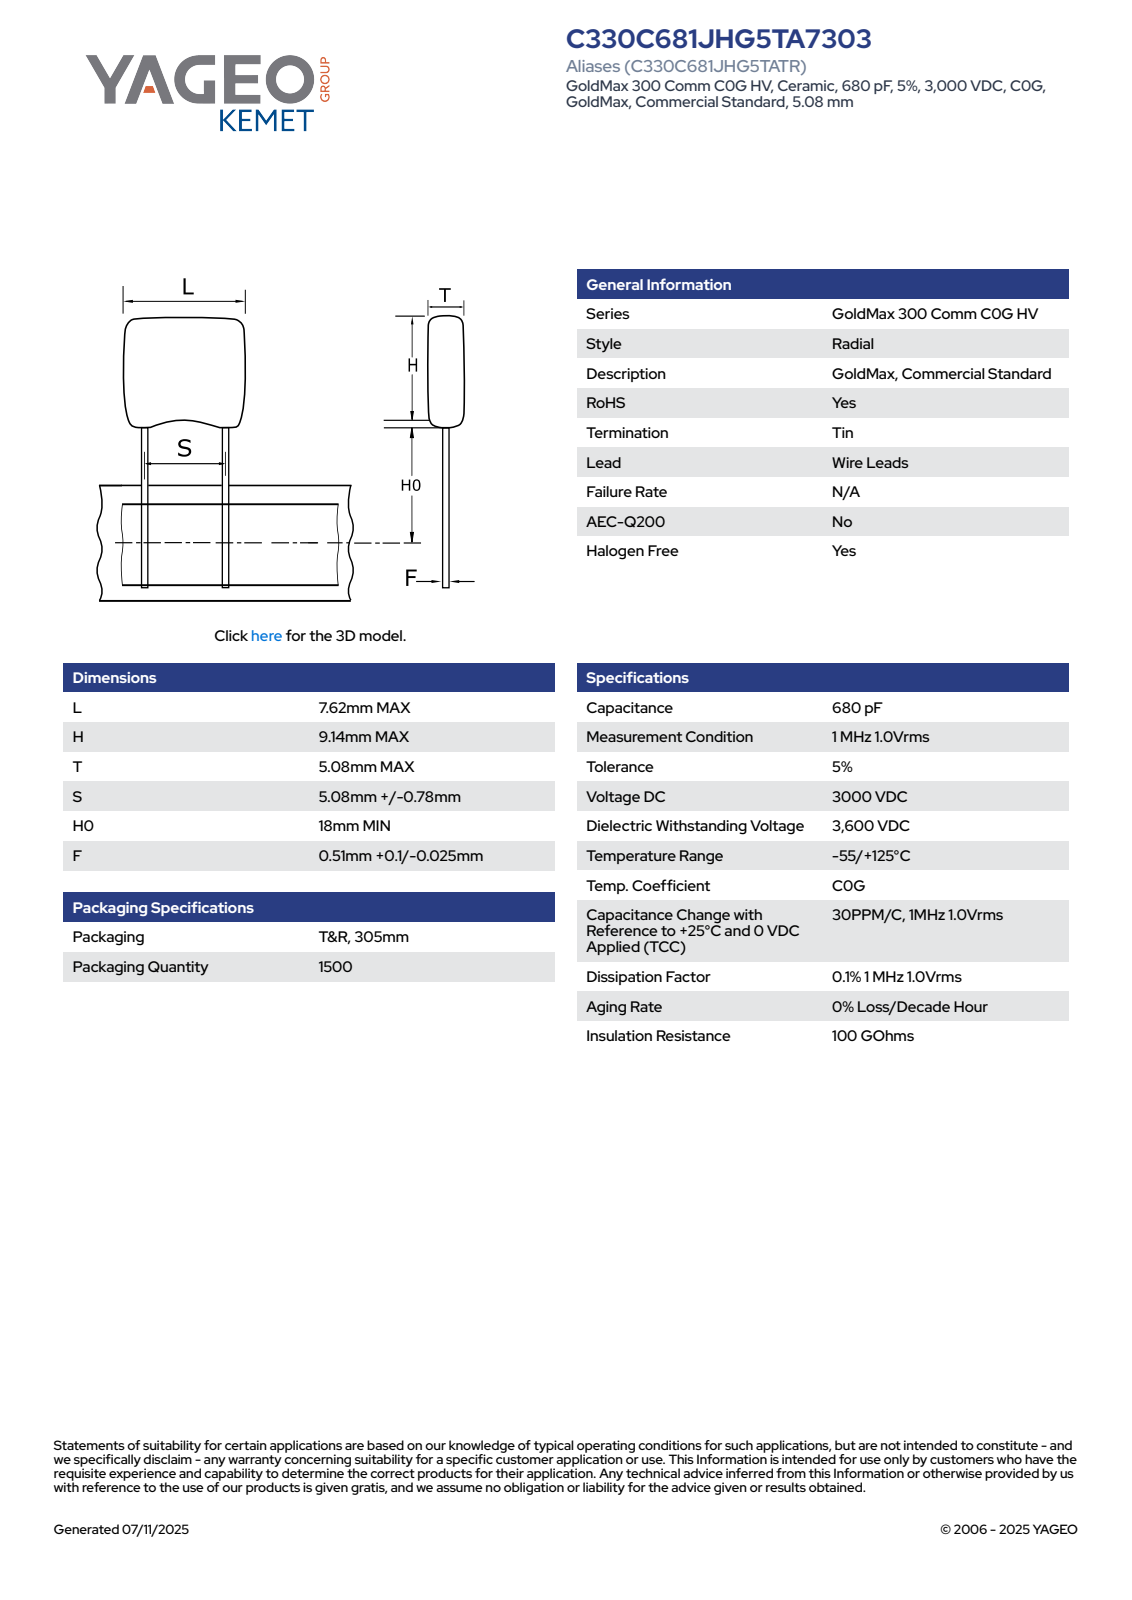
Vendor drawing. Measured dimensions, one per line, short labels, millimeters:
name: CCR_KRCST_7.62X9.14_L7.62H9.14T5.08S5.08H018F0.61
written by: SolidWorks 2014 (AUTOMOTIVE_DESIGN)
unit: mm
bodies: 4 solids, 83 faces (65 planar, 14 cylindrical, 4 other)
size: 28.18 × 7.62 × 5.08
volume: 395 mm³; area: 382 mm²
bosses: 2× ⌀0.61
rounds: 10× R0.75
face distances: 5.08, 7.62, 10.18, 18, 28.18, 23.33, 5.33, 4.85, 22.52, 4.52
